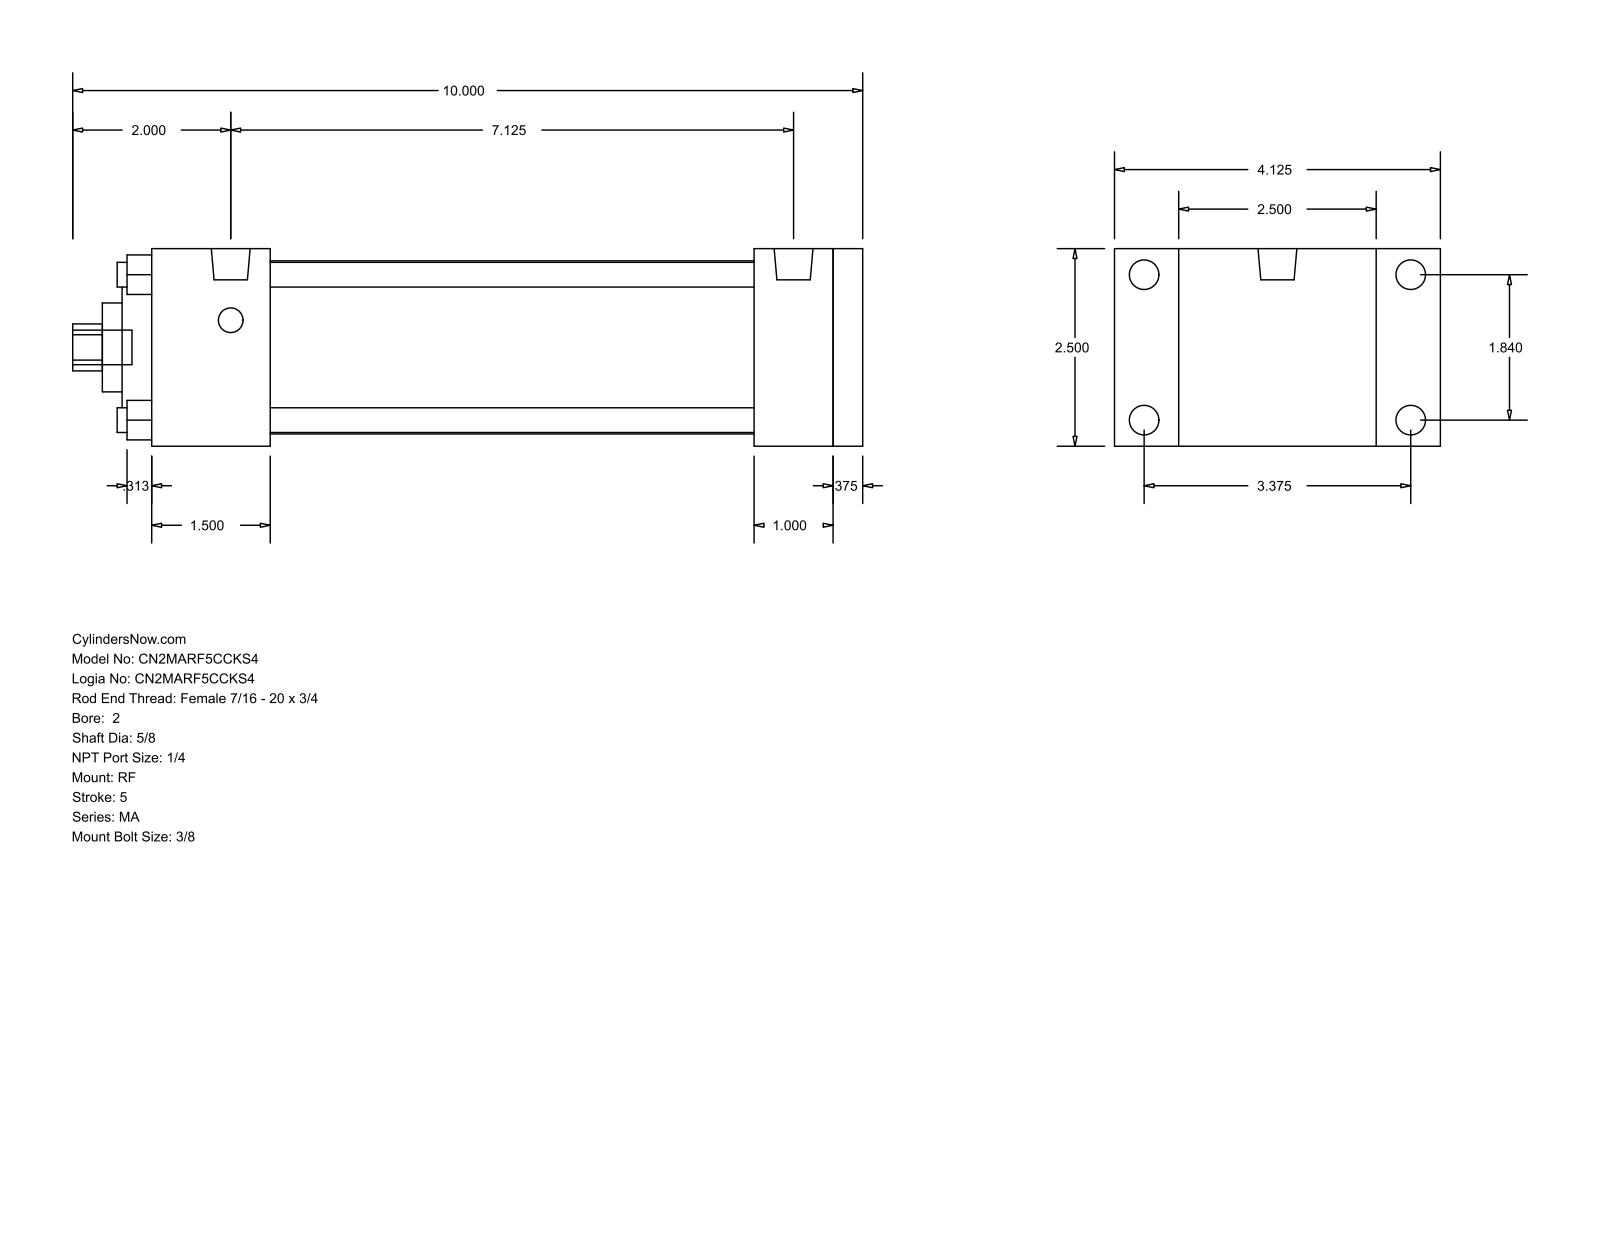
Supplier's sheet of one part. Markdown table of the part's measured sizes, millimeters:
| quantity | value |
| --- | --- |
| part name | MA_RF__0200_0.625 |
| STEP written by | GSSL Pune (CONFIG_CONTROL_DESIGN) |
| units | millimeters |
| bodies | 0 solids, 94 faces (65 planar, 29 cylindrical, 0 other) |
| overall size | 254 × 104.78 × 63.5 |
| round holes (diameter × count) | 7.94 × 4, 15.88 × 1, 28.57 × 1, 50.8 × 1, 55.63 × 1 |
| round bosses / shafts (diameter × count) | 9.53 × 4, 7.94 × 4, 12.49 × 2, 11.11 × 1 |
| partial cylindrical surfaces (radius × count) | 7.54 × 1 |
| main face-to-face distances | 63.5, 9.53, 25.4, 38.1, 219.07, 9.52, 228.6, 238.12, 180.97, 190.5 |
| hole center spacings | 33.05, 46.74, 66.1 |
